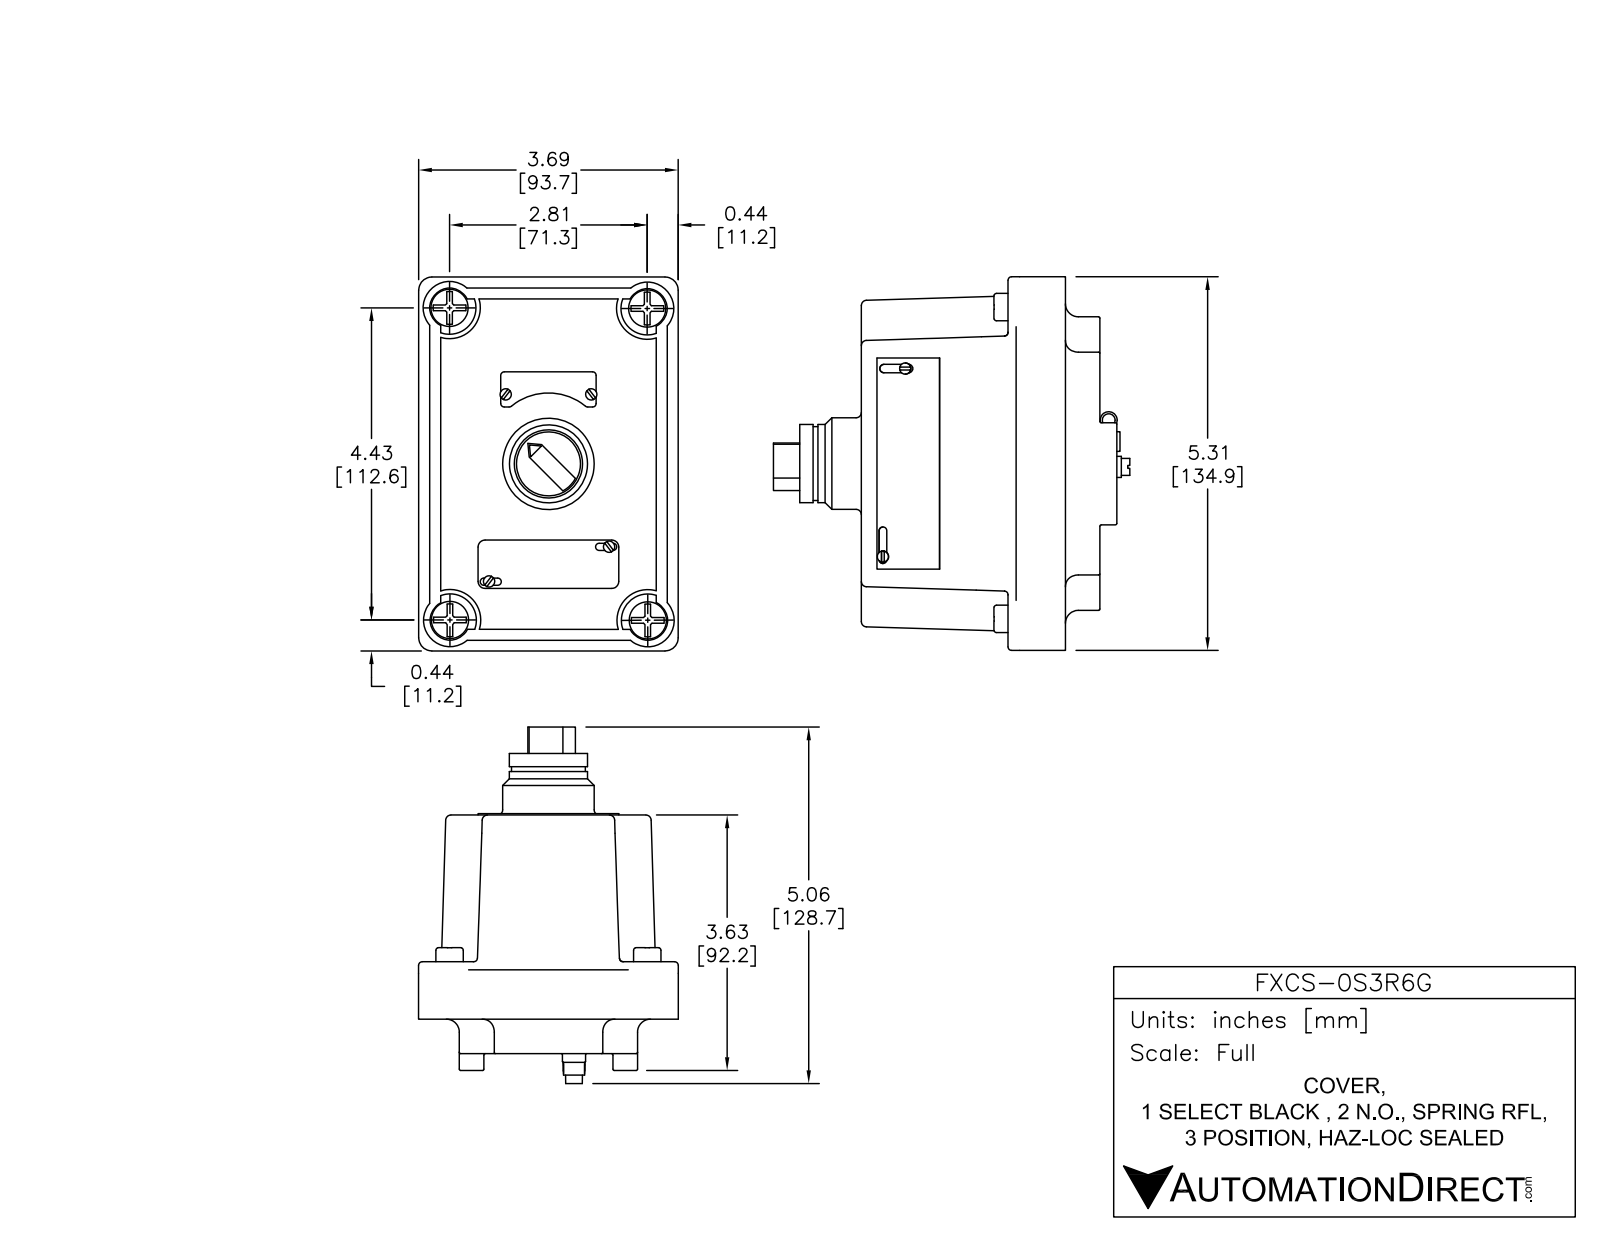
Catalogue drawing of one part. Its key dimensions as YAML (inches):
part_name: "FXCS-0S3R6G"
step_written_by: "SolidWorks 2015 (AUTOMOTIVE_DESIGN)"
units: inches
bodies: {solids: 2, faces: 710, planar: 308, cylindrical: 166, other: 236}
overall_size: [5.31, 5.066, 3.69]
volume: 48.91
surface_area: 100.9
round_holes:
  - {diameter: 0.16, count: 8}
  - {diameter: 0.198, count: 1}
  - {diameter: 0.97, count: 1}
round_bosses_or_shafts:
  - {diameter: 0.16, count: 8}
  - {diameter: 0.39, count: 4}
  - {diameter: 1.3, count: 1}
  - {diameter: 1.11, count: 1}
  - {diameter: 1.05, count: 1}
  - {diameter: 0.91, count: 1}
  - {diameter: 0.33, count: 1}
  - {diameter: 0.3, count: 1}
partial_cylinders:
  - {radius: 0.05, count: 24}
  - {radius: 0.02, count: 22}
  - {radius: 0.051, count: 4}
  - {radius: 0.055, count: 4}
  - {radius: 0.06, count: 4}
  - {radius: 0.075, count: 4}
  - {radius: 0.1, count: 4}
  - {radius: 0.185, count: 4}
face_to_face_distances: [3.39, 0.49, 2.9, 0.021, 3.69, 0.578, 3.111, 1.19, 0.7, 2.2]
hole_center_spacings: [0.25, 2.197, 0.5, 2.183, 2.239, 0.75, 1.092, 1.115]
